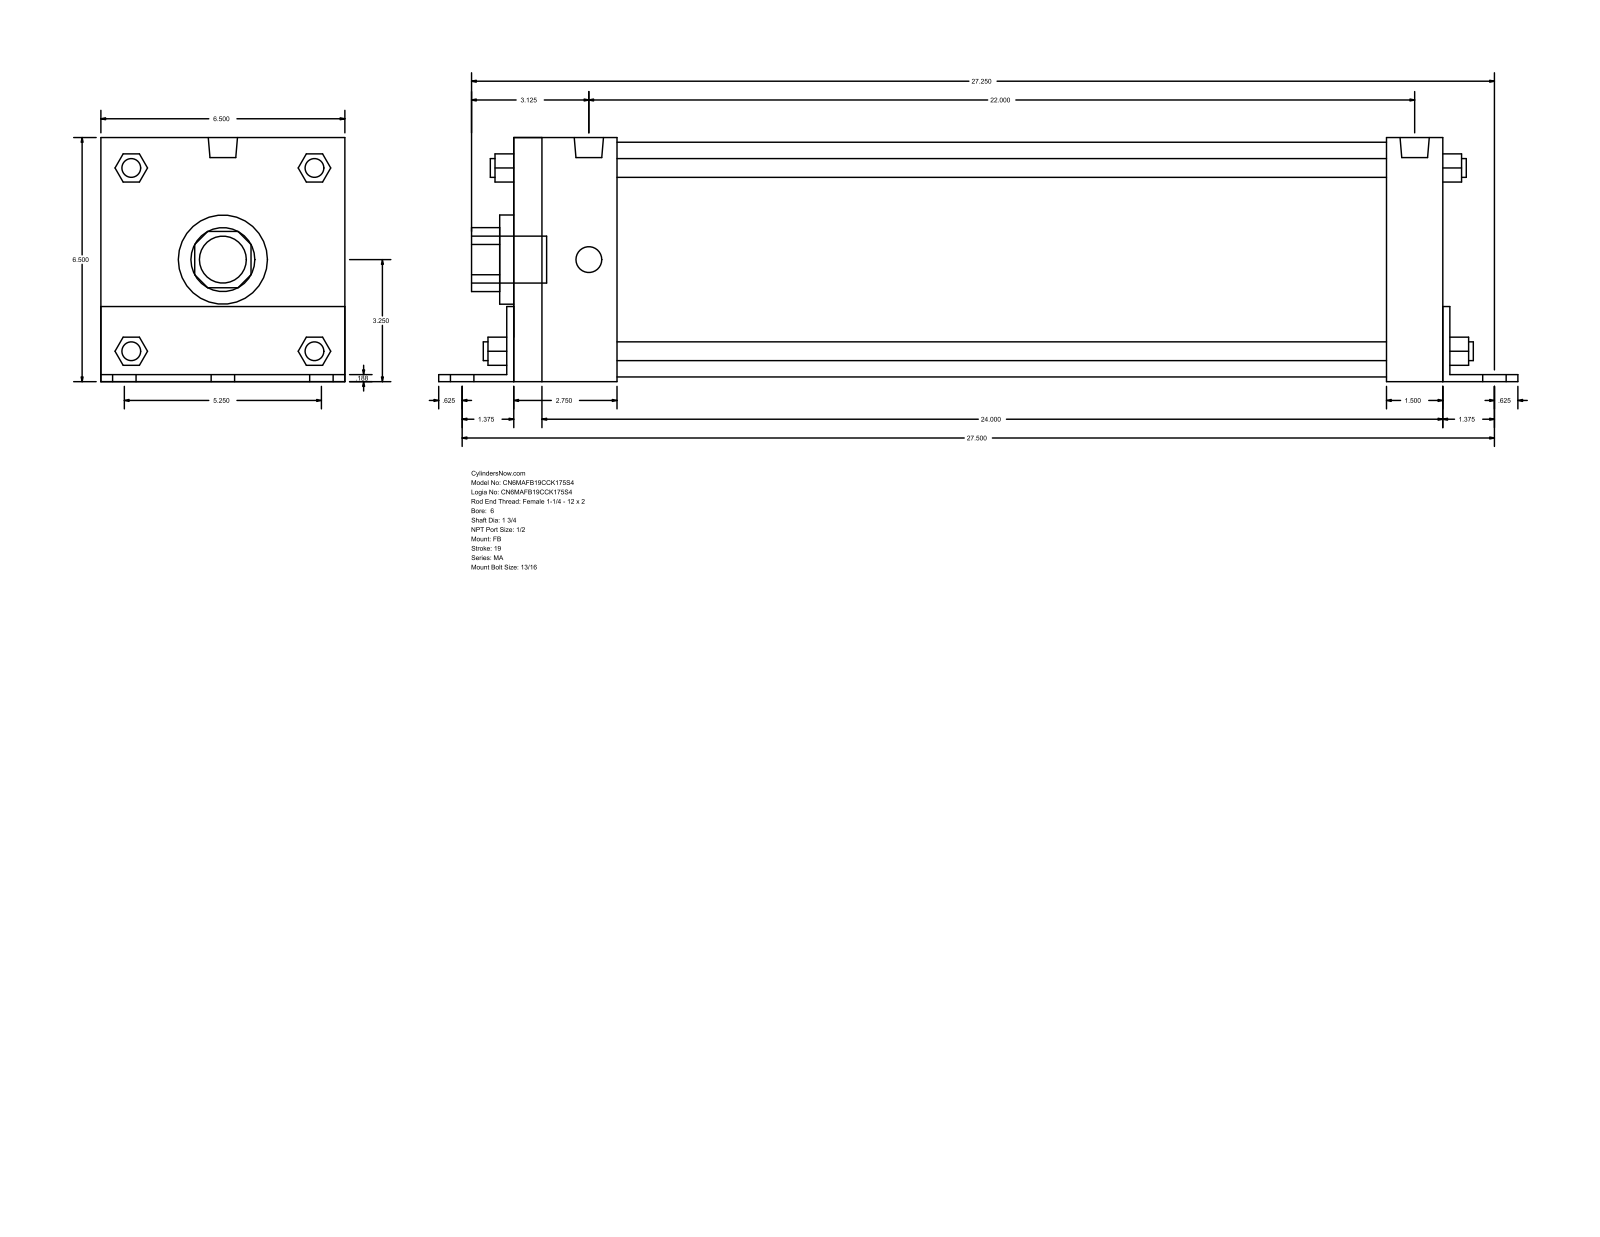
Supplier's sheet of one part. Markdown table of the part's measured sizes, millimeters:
| quantity | value |
| --- | --- |
| part name | MA_FB__0600_1.75 |
| STEP written by | GSSL Pune (CONFIG_CONTROL_DESIGN) |
| units | millimeters |
| bodies | 0 solids, 140 faces (105 planar, 35 cylindrical, 0 other) |
| overall size | 730.25 × 165.15 × 165.1 |
| round holes (diameter × count) | 44.45 × 1, 60.33 × 1, 158.75 × 1 |
| round bosses / shafts (diameter × count) | 20.64 × 6, 17.46 × 4, 12.7 × 4, 19.77 × 2, 31.75 × 1 |
| partial cylindrical surfaces (radius × count) | 21.63 × 1, 32.05 × 1 |
| main face-to-face distances | 165.1, 4.76, 628.66, 165.15, 633.42, 4.71, 160.39, 638.18, 38.11, 74.61 |
